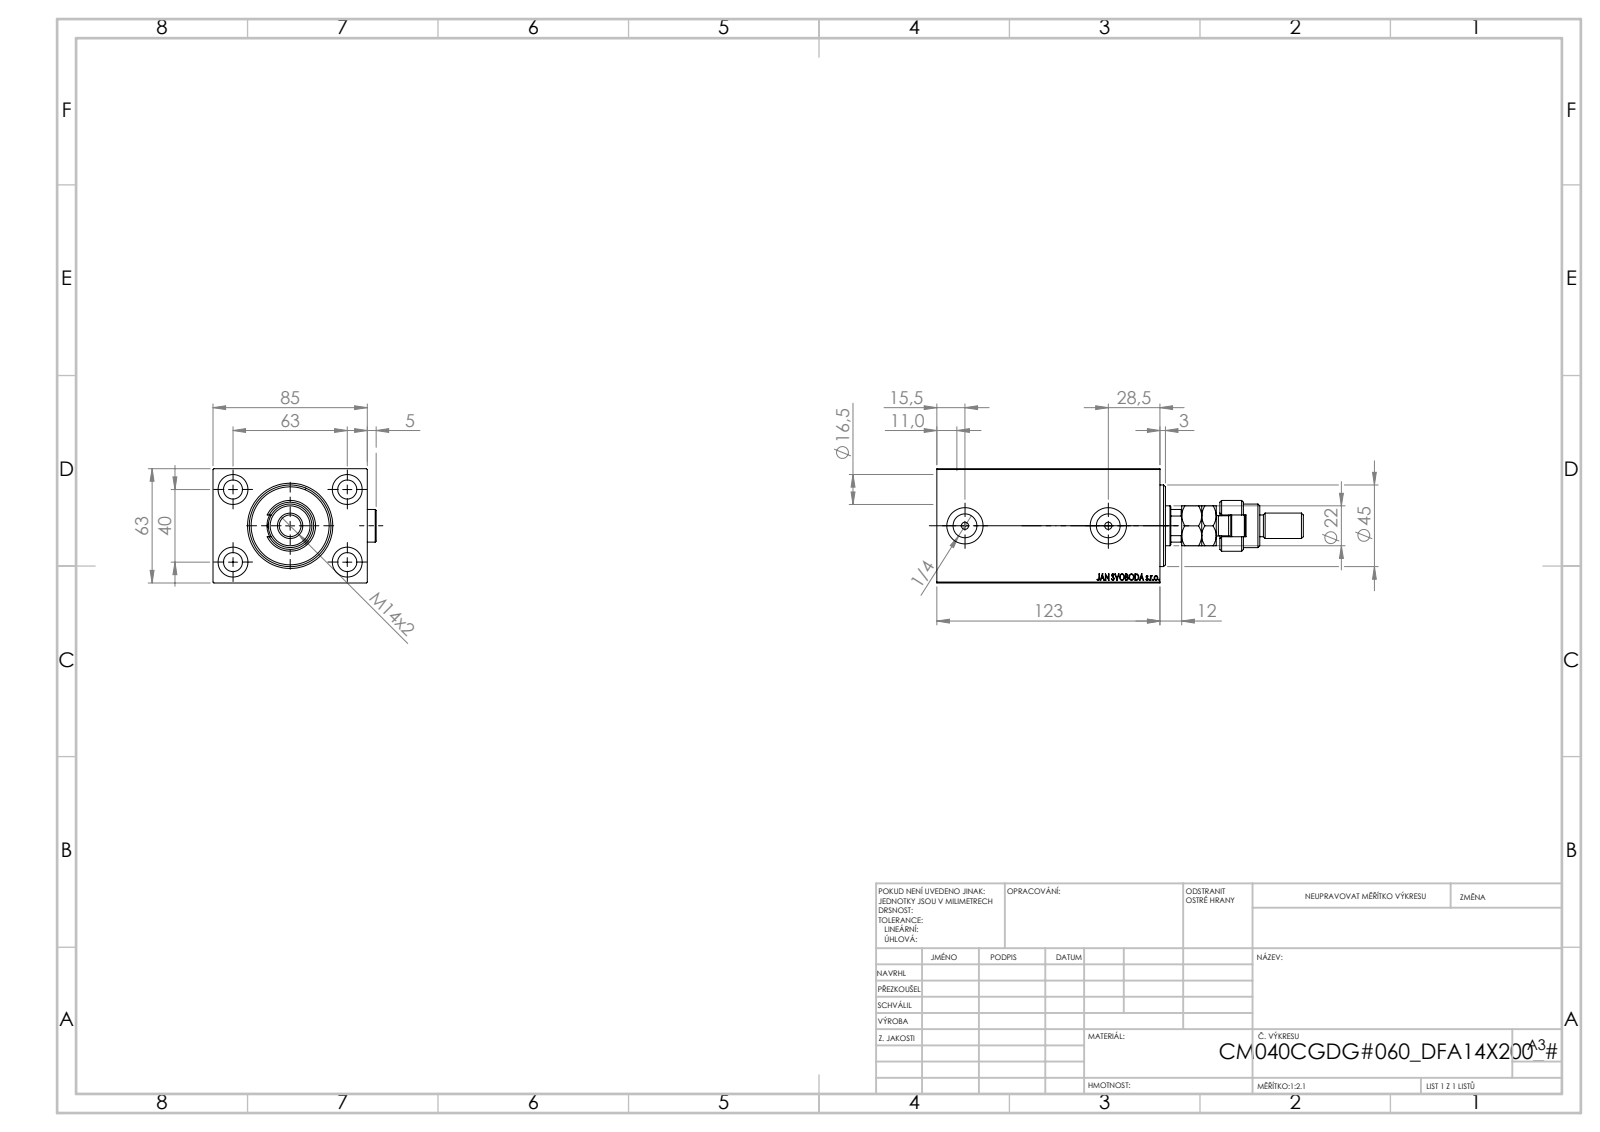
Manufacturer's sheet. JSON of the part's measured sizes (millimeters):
{"part_name": "V450CM_C_VCP; FEMALE_PART_FOR_DFA; V450CM_VC_B; V450CM_C_Body (+2 more)", "step_written_by": "SolidWorks 2019 (CONFIG_CONTROL_DESIGN)", "units": "millimeters", "bodies": {"solids": 7, "faces": 1001, "planar": 470, "cylindrical": 89, "other": 442}, "overall_size": [202, 89.9, 63], "volume_mm3": 573650, "surface_area_mm2": 109854, "round_holes": [[10.5, 4], [16.5, 4], [4, 2], [13.16, 2], [20, 2], [12.5, 1], [22, 1], [25.5, 1], [40, 1], [42, 1], [45, 1]], "round_bosses_or_shafts": [[18, 3], [28, 1], [24, 1], [14, 1], [12, 1], [11, 1]], "partial_cylinders_radius": [[9.75, 1], [10.5, 1]], "face_to_face_distances": [63, 85, 12, 111, 123, 84.9, 3, 60, 15, 99], "hole_center_spacings": [37.31, 40, 63, 74.63, 79]}
